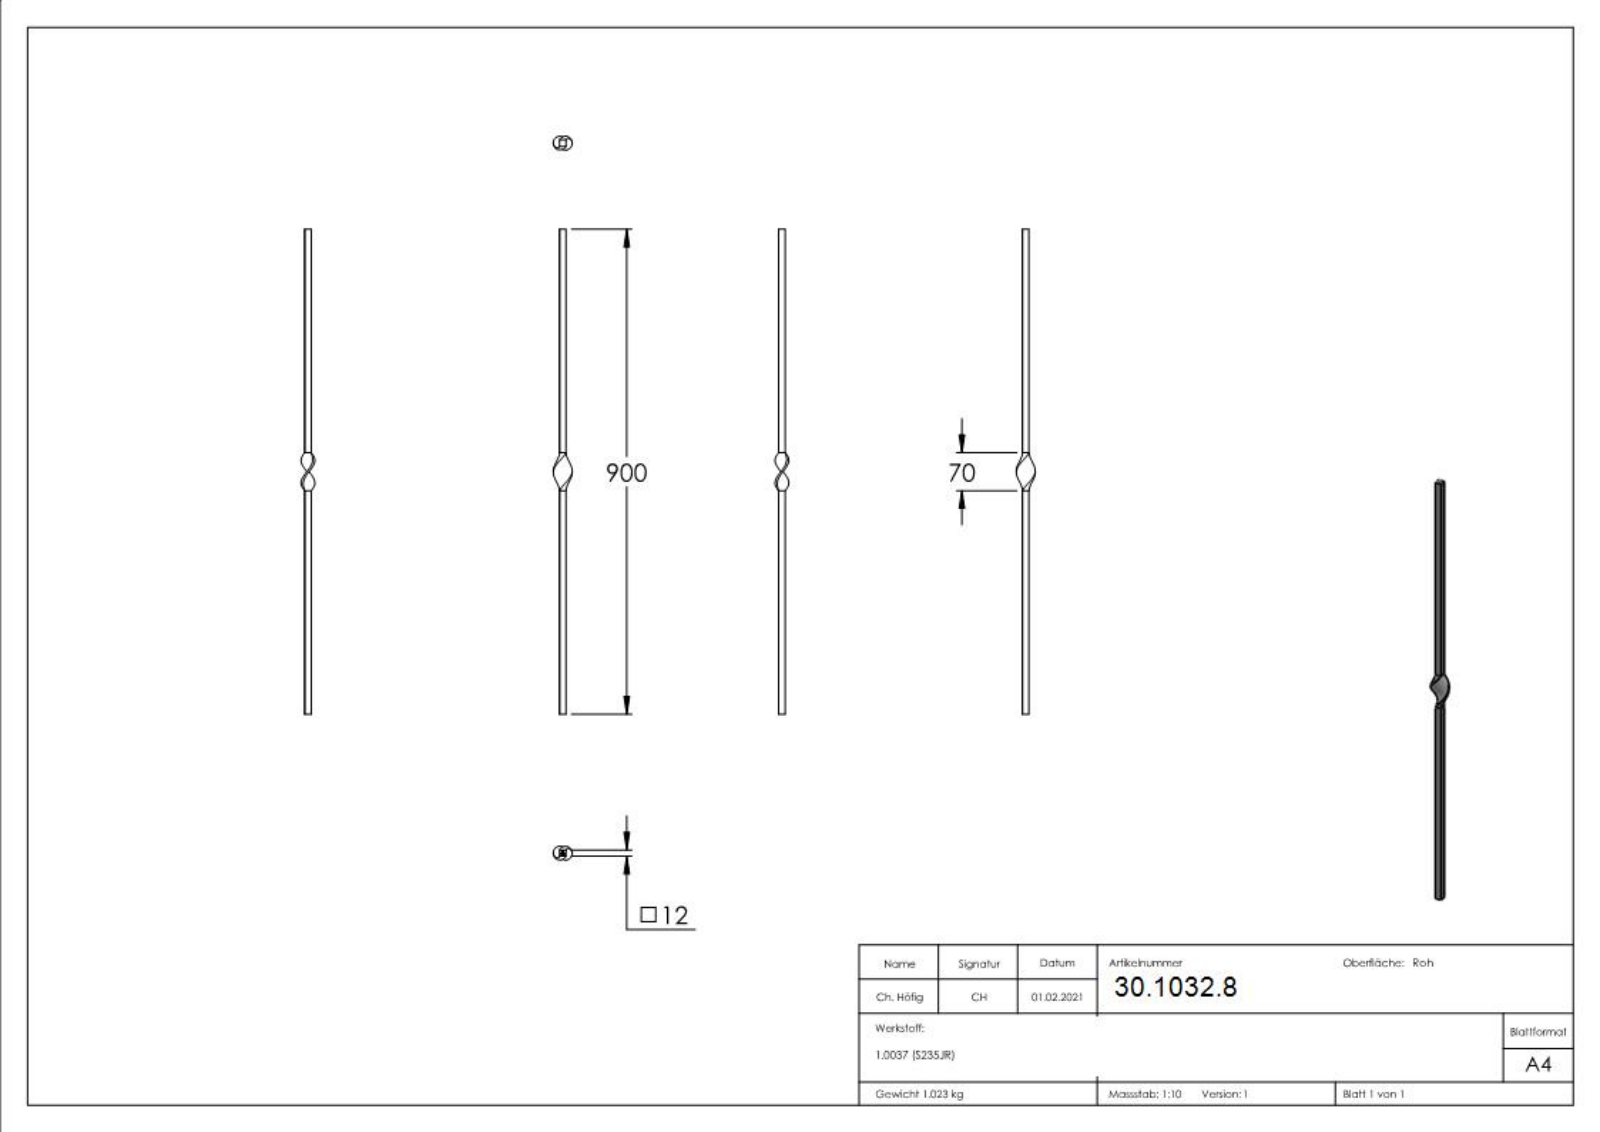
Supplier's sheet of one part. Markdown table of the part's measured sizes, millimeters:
| quantity | value |
| --- | --- |
| part name | 1102 |
| STEP written by | SolidWorks 2018 (CONFIG_CONTROL_DESIGN) |
| units | millimeters |
| bodies | 1 solid, 206 faces (119 planar, 0 cylindrical, 87 other) |
| overall size | 900 × 35.67 × 25.66 |
| volume | 131 140 mm³ |
| surface area | 45 275 mm² |
| main face-to-face distances | 12, 900, 899.9, 0.69, 5, 7, 0.33, 2.23, 2.7, 1.54 |
